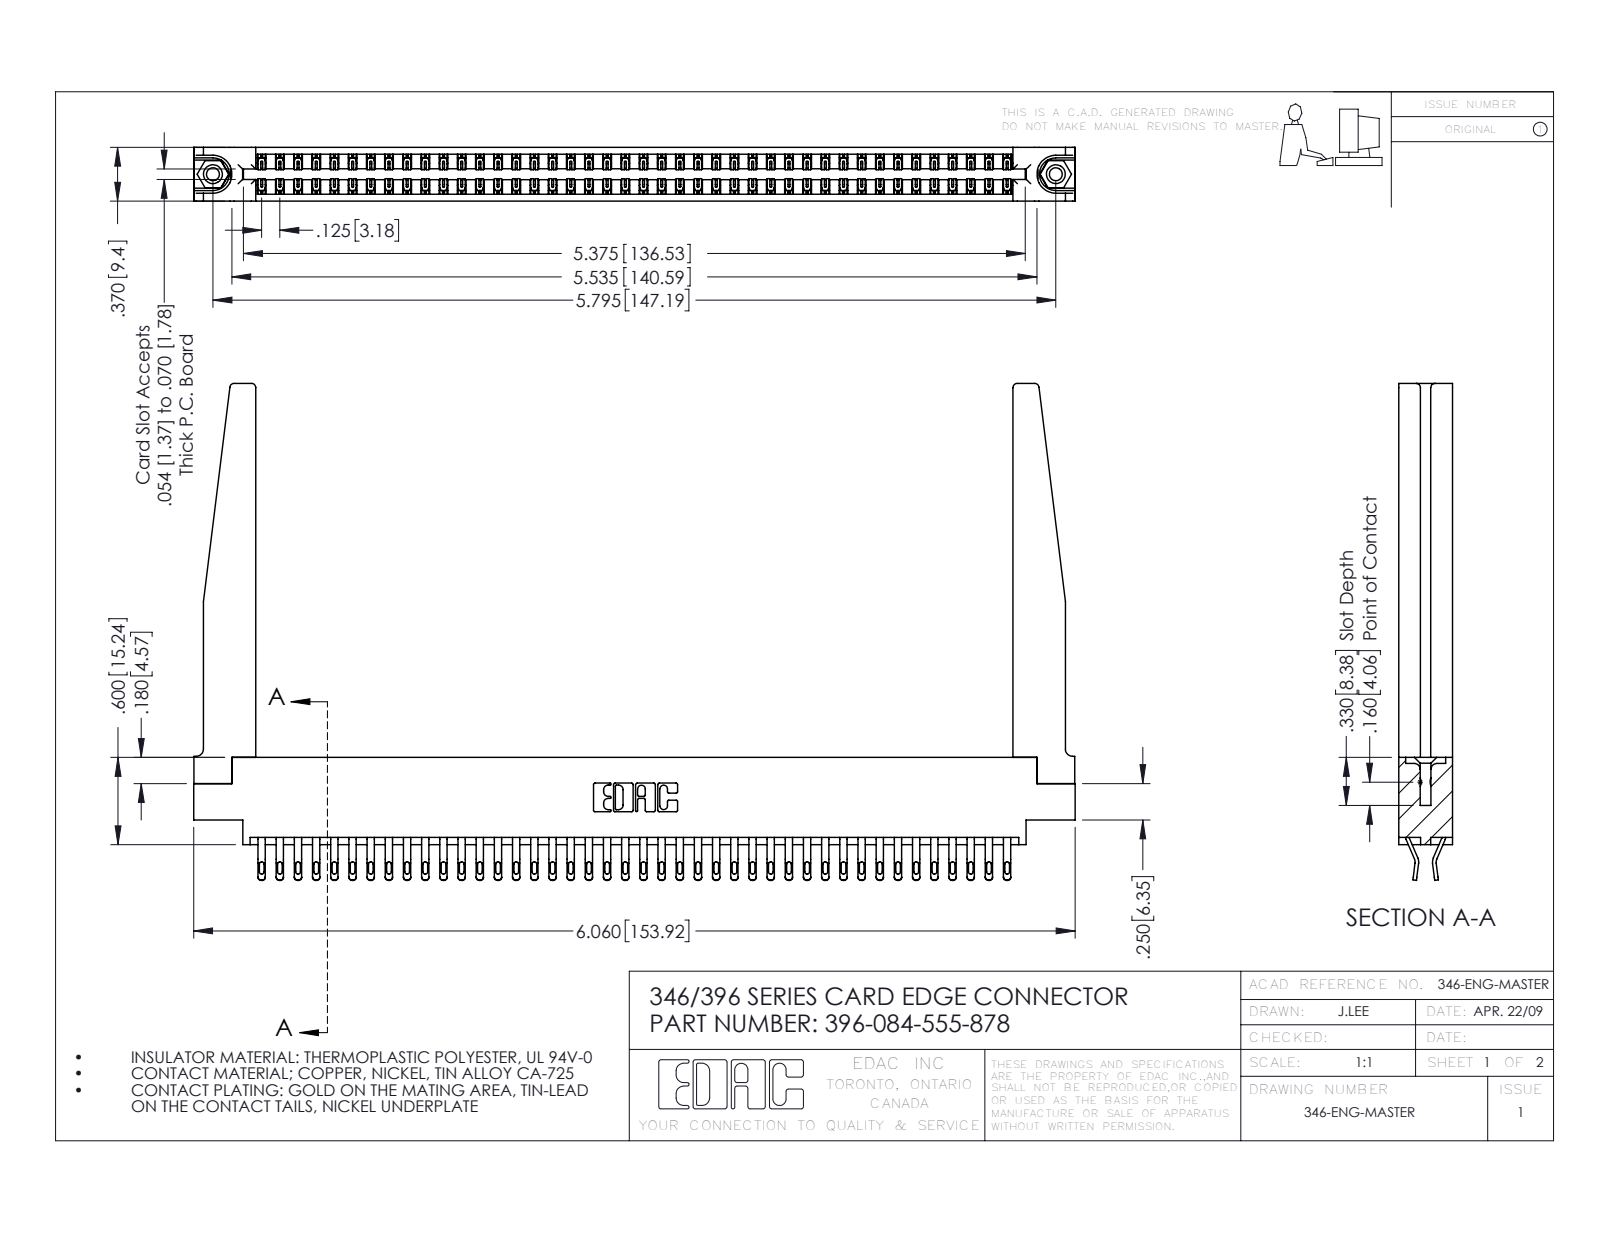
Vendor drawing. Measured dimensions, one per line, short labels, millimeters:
name: 345-292-001_555 Tail; 346-220-078_345-220-078; 345-250-001_345-250-001-102; 346 Part_0.170 Offset - 0.156 Dia-TH (+1 more)
written by: SolidWorks 2016 (CONFIG_CONTROL_DESIGN)
unit: mm
bodies: 89 solids, 5232 faces (2994 planar, 2186 cylindrical, 52 other)
size: 153.9 × 86.7 × 9.4
volume: 22 010 mm³; area: 28 340 mm²
holes: 2× ⌀2.3, 2× ⌀3.2, 2× ⌀4, 1× ⌀1.6
bosses: 2× ⌀3.9
rounds: 168× R0.4, 168× R0.5, 126× R0.2, 22× R0.3, 8× R0.8, 6× R0.2, 6× R0.8, 4× R1.3
face distances: 9.4, 1.2, 8.2, 1.8, 3.8, 3.8, 6.4, 0.6, 7.6, 7
hole spacings: 6.2, 141.9, 147.2
